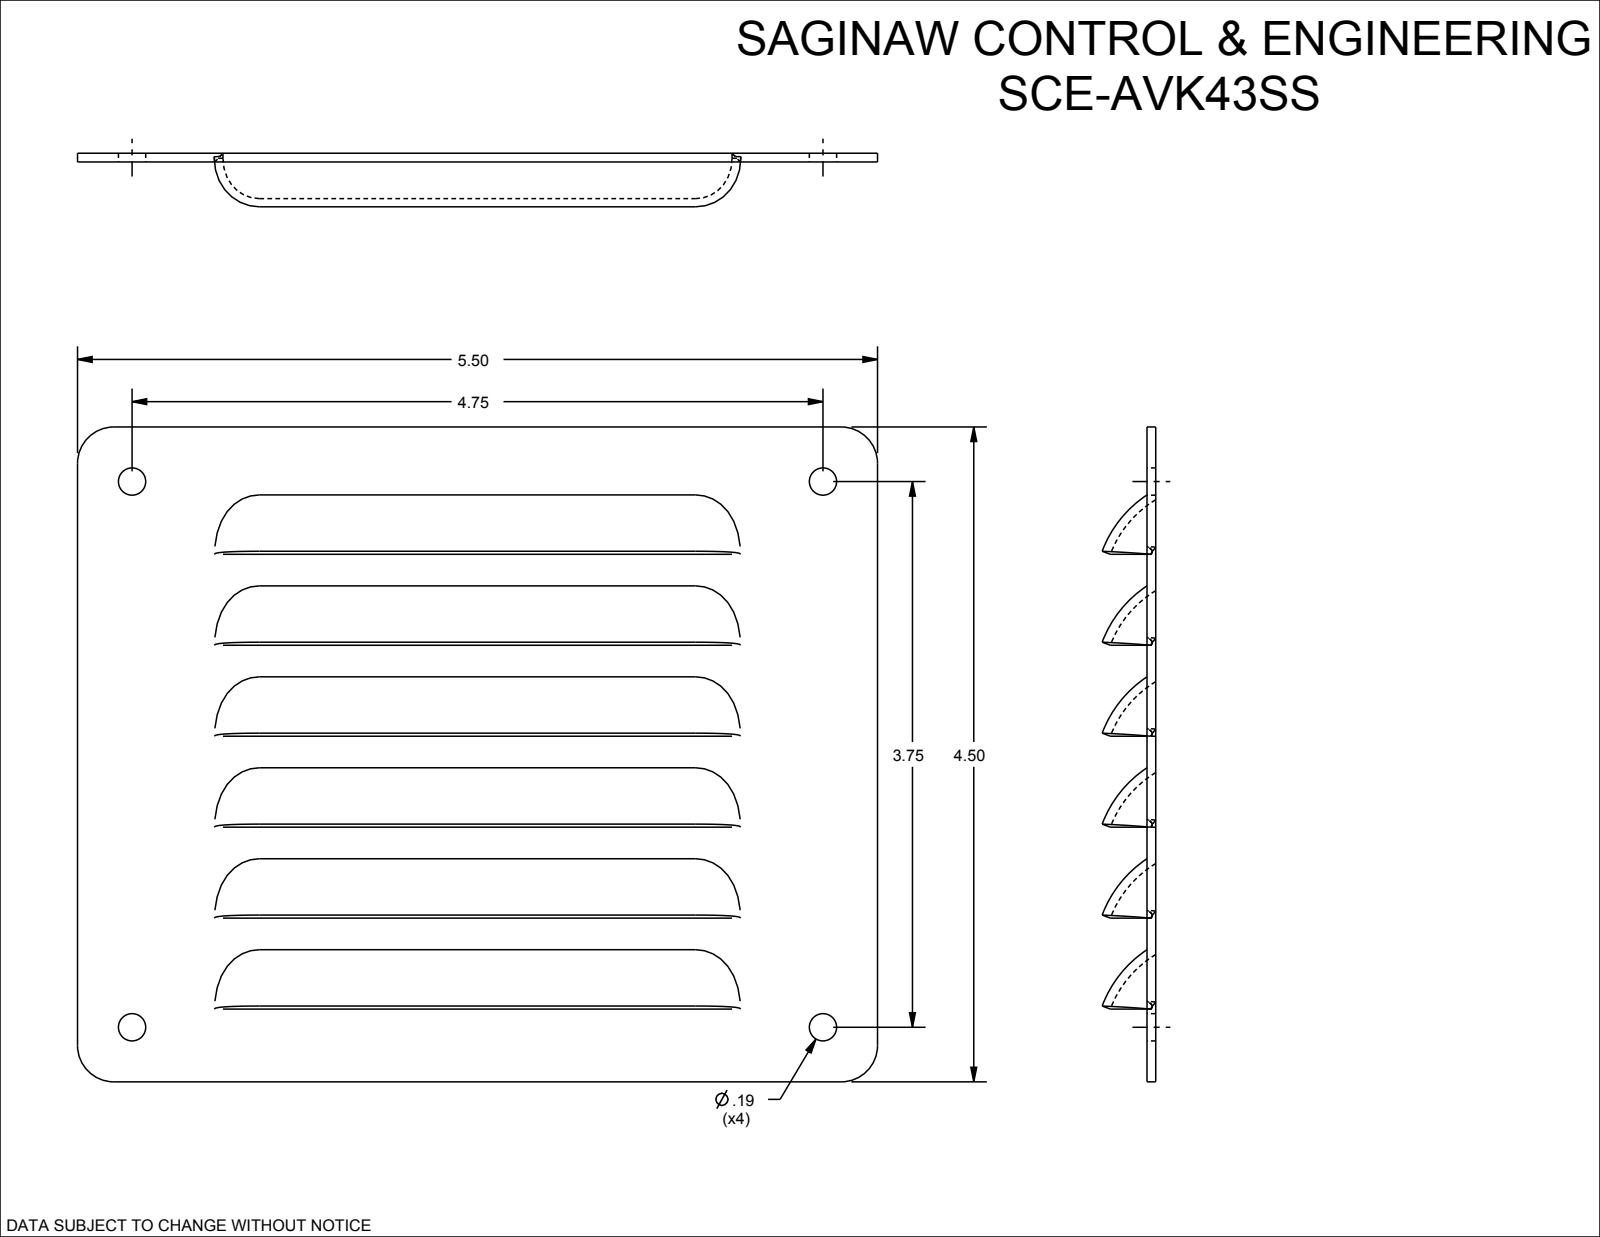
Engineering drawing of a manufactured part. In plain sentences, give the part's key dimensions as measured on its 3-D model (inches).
The part is named "SCE-AVK43". Its 3-D file was written by "SolidWorks 2021 (AUTOMOTIVE_DESIGN)". It is 1 solid with 108 faces: 24 planar, 36 cylindrical and 48 other. Overall it measures 5.5 by 4.5 by 0.467 inches. Its volume is 1.66 cubic inches and its surface area 58.98 square inches. Round holes: 4 of diameter 0.187. Partial cylindrical surfaces (rounded edges, fillets, slot ends): 6 of radius 0.74, 6 of radius 0.8, 4 of radius 0.25. The main face-to-face distances are 0.06, 1.25, 0.625, 0.625, 0.29, 0.96, 2.5, 1.171, 1.875, 1.875. The hole center spacings are 3.75, 4.75, 6.051.
